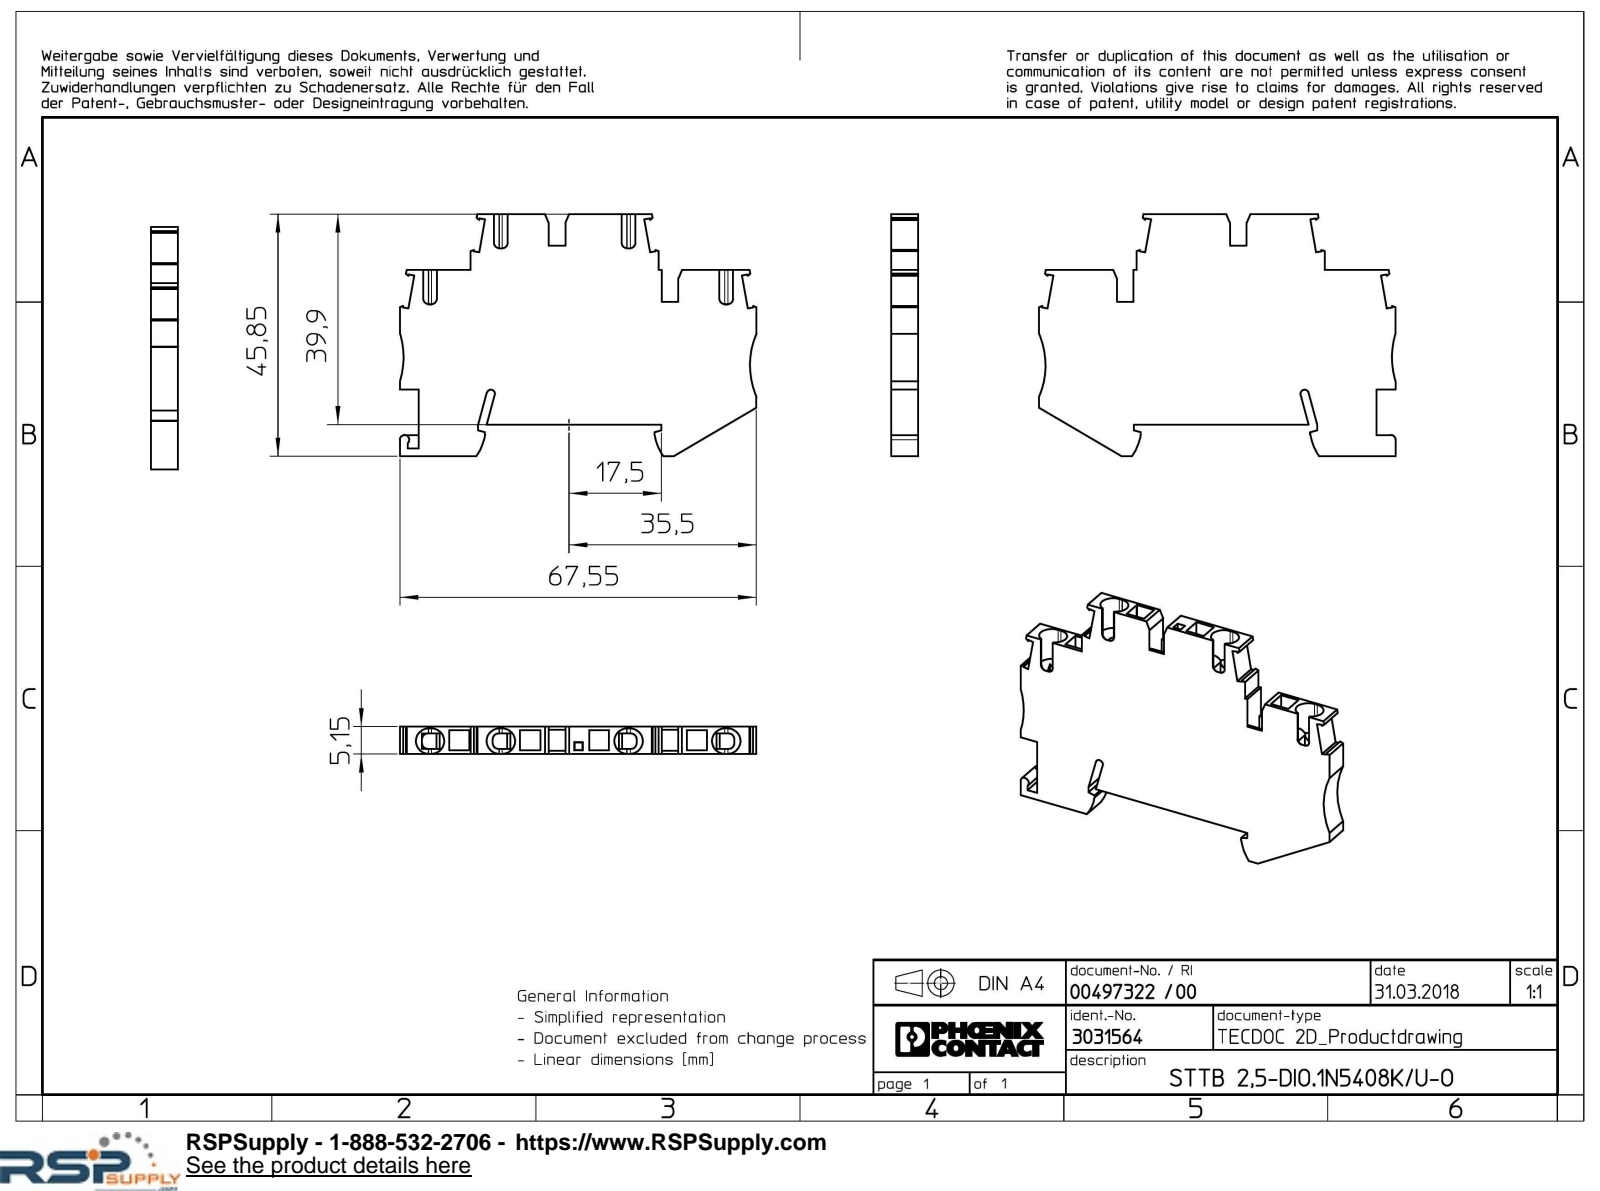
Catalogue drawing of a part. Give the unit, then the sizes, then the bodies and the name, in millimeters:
Units: millimetres
Overall size (bounding box): 67.55 × 45.85 × 5.15
Partial cylindrical surfaces — rounded edges, fillets, slot ends (radius × count): R1 ×16, R2.4 ×8, R9.5 ×2, R15 ×2, R0.8 ×1, R0.9 ×1, R11.94 ×1
Main face-to-face distances: 5.15, 3.15, 0.65, 21.4, 3.8, 4.5, 29.25, 4.45, 4, 13.2
Volume: 10 426 mm³ · Surface area: 7 639 mm²
Bodies: 1 solid, 202 faces (159 planar, 31 cylindrical, 12 other)
Part name (STEP PRODUCT): STTB25-....-Select
STEP written by: Creo Elements/Direct Modeling 20.1A 29-Sep-2018 (C) Parametric Technology GmbH (AUTOMOTIVE_DESIGN)
